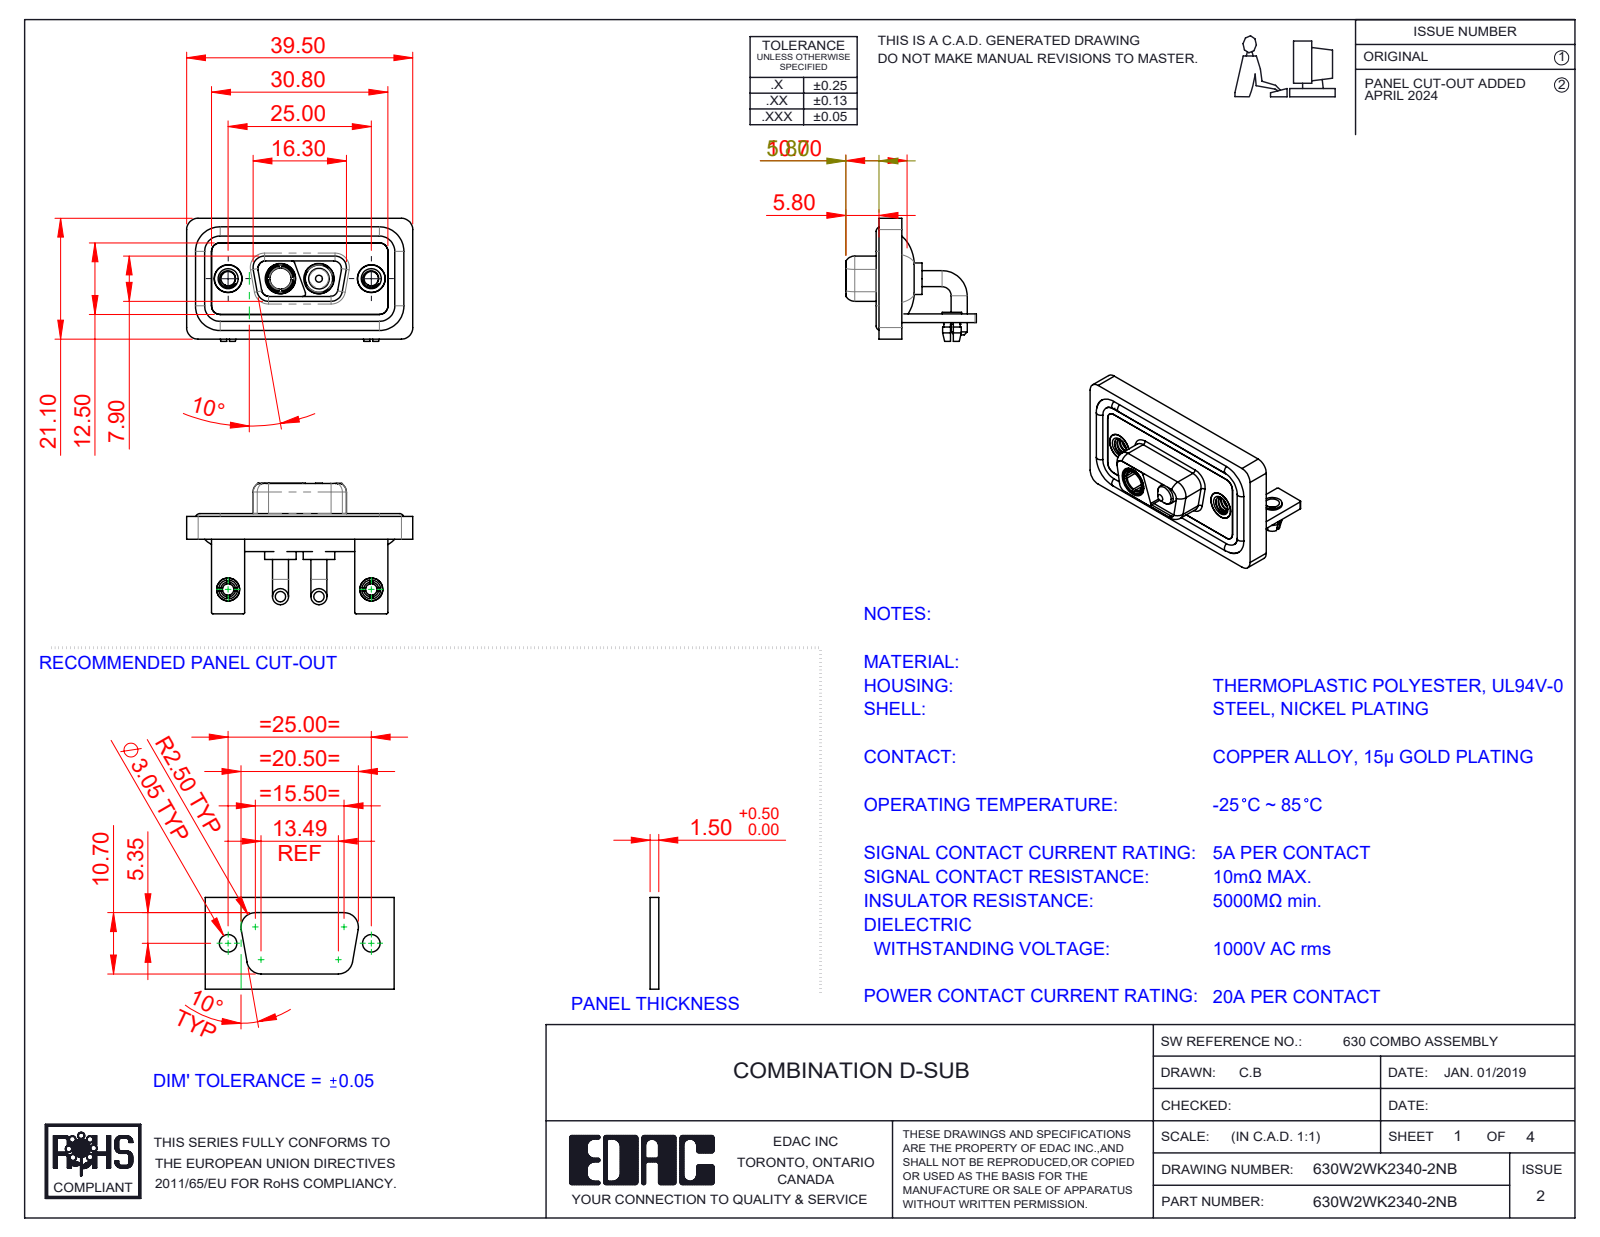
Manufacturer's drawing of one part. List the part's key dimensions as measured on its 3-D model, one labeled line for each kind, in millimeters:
Part name (STEP PRODUCT): 630Combo Stabilizer Bracket_50 Contacts; 630Combo Shell Front_09 Contacts; Power Socket_20A RA; 630Combo Shell Rear_09 Contacts (+6 more)
STEP written by: SolidWorks 2023 (CONFIG_CONTROL_DESIGN)
Units: millimetres
Bodies: 15 solids, 642 faces (212 planar, 289 cylindrical, 141 other)
Overall size (bounding box): 39.5 × 22.8 × 21.5
Volume: 5 102 mm³ · Surface area: 8 443 mm²
Round holes (diameter × count): ⌀2.5 ×4, ⌀4.85 ×4, ⌀2 ×2, ⌀3.2 ×2, ⌀4 ×2, ⌀4.05 ×2, ⌀5 ×2, ⌀5.3 ×2, ⌀3.7 ×1
Round bosses / shafts (diameter × count): ⌀2.8 ×4, ⌀1.6 ×4, ⌀5.5 ×2, ⌀5.2 ×2, ⌀4.95 ×2, ⌀4.8 ×2, ⌀4.75 ×2, ⌀4 ×2
Partial cylindrical surfaces — rounded edges, fillets, slot ends (radius × count): R2 ×19, R1.5 ×18, R0.25 ×16, R1.35 ×8, R1.6 ×8, R0.5 ×7, R0.6 ×4, R0.65 ×4
Main face-to-face distances: 0.4, 2.9, 1.5, 1.1, 3.7, 1.8, 0.8, 2.5, 1.6, 3.1
Hole centre spacings: 9.14, 15.86, 25, 6.72
